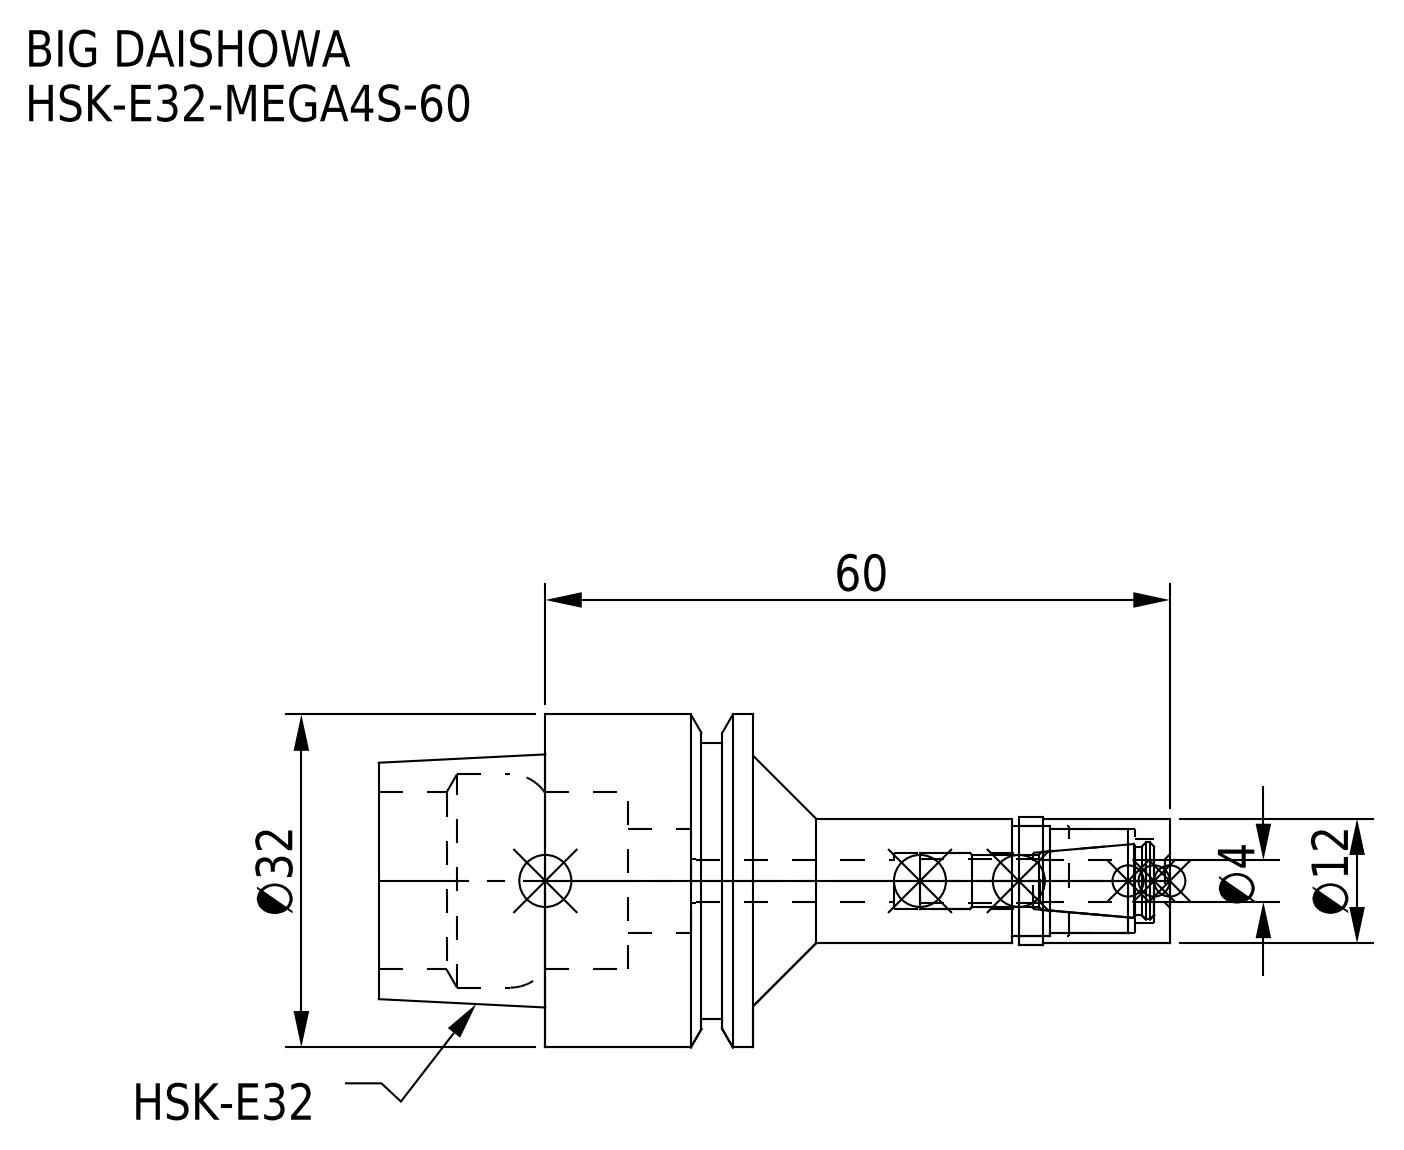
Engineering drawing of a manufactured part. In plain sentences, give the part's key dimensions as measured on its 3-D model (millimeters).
The part is named "HE32MS04060-040_ASM.stp; HSK-E32-MEGA4S-60_1.stp; MGN4S_1.stp; HSK-E32-MEGA4S-60-040-FreeParts (+3 more)". Its 3-D file was written by "SolidWorks 2019 (CONFIG_CONTROL_DESIGN)". It is 2 solids with 74 faces: 18 planar, 40 cylindrical and 16 other. Overall it measures 76 by 32 by 32 millimeters. Its volume is 20 037 cubic millimeters and its surface area 9 713 square millimeters. Round holes: 1 of diameter 4.1, 1 of diameter 4.2, 1 of diameter 5.4, 1 of diameter 8, 1 of diameter 10, 1 of diameter 10.5, 1 of diameter 17, 1 of diameter 20.5. Round bosses or shafts: 1 of diameter 32, 1 of diameter 26.5, 1 of diameter 12.3, 1 of diameter 12. The main face-to-face distances are 20, 36, 16, 12.05, 7.95, 23.95, 3, 15, 40, 52.05.
